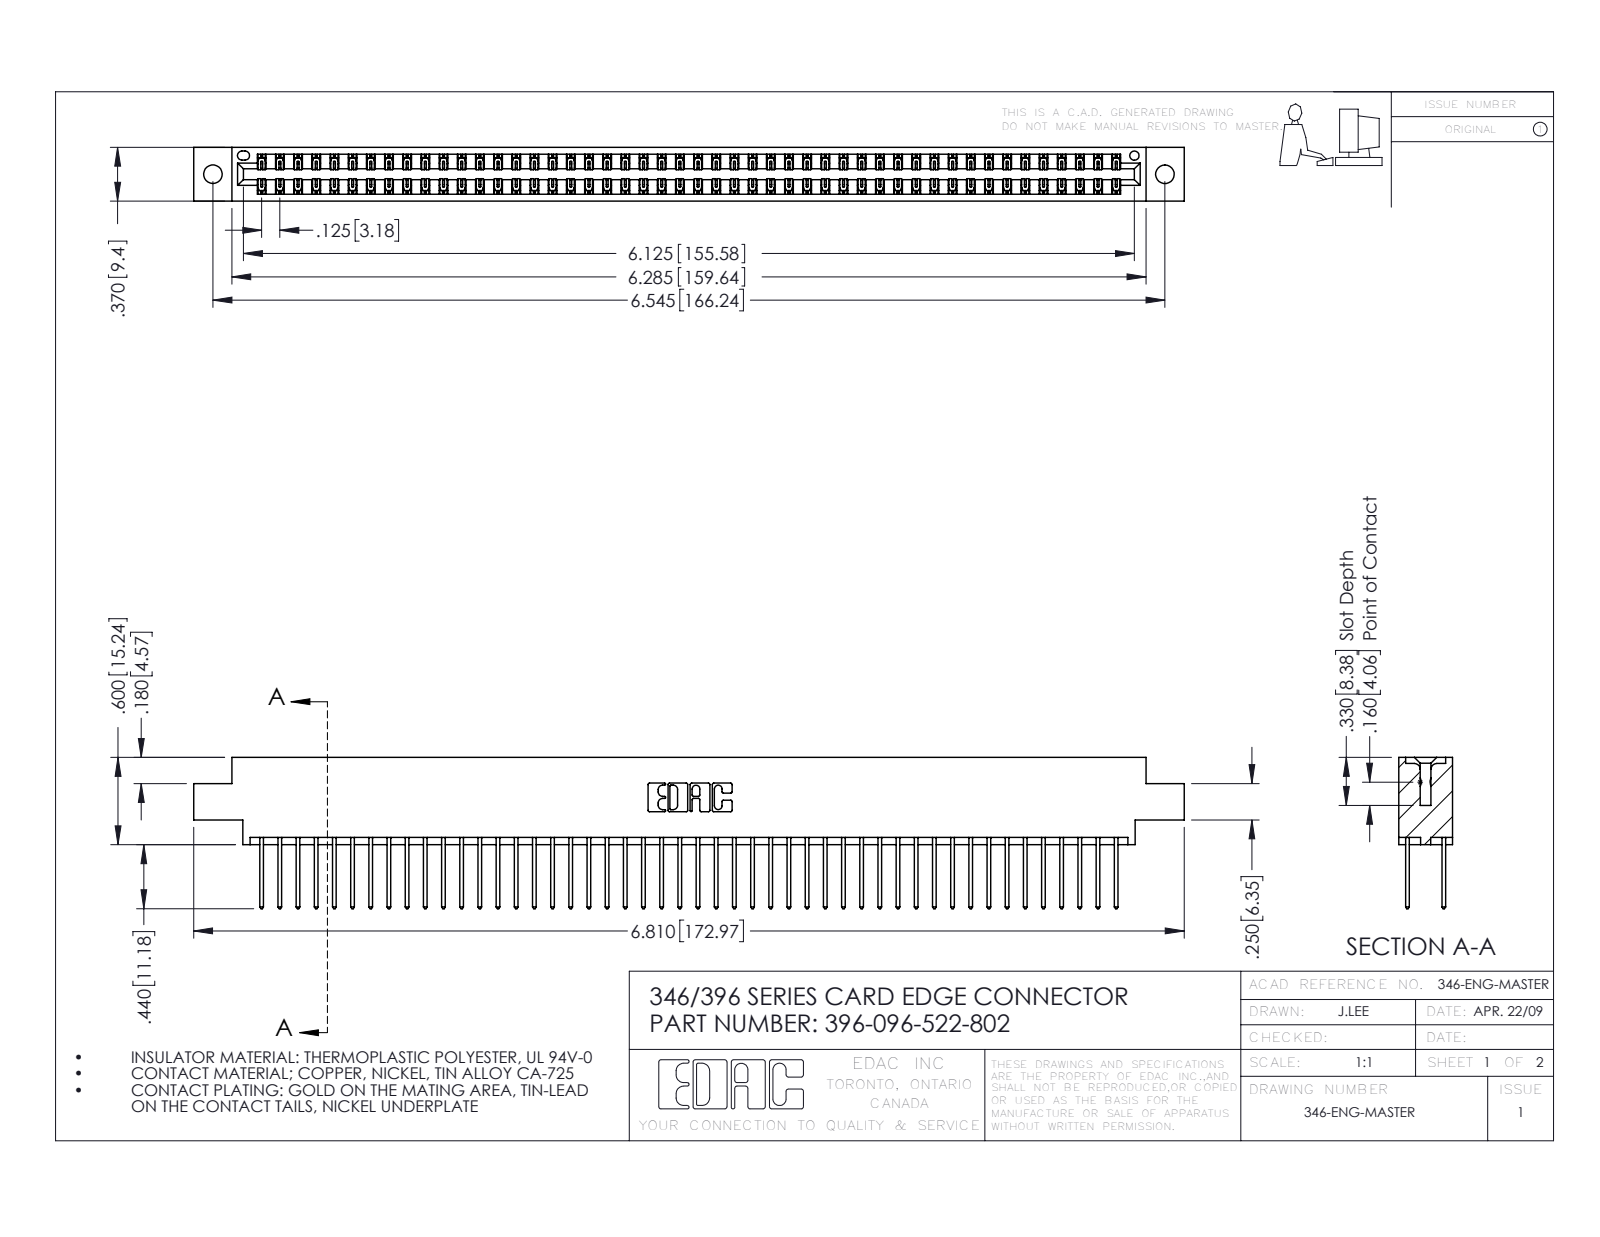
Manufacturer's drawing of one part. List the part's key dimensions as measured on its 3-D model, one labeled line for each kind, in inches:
Part name (STEP PRODUCT): 396-096-522-802; 346 Part_0.170 Offset - 0.128 Dia; 345-292-001_345-293-122
STEP written by: SolidWorks 2016 (CONFIG_CONTROL_DESIGN)
Units: inches
Bodies: 97 solids, 5118 faces (3440 planar, 1678 cylindrical, 0 other)
Overall size (bounding box): 6.81 × 1.04 × 0.37
Volume: 1.035 in³ · Surface area: 37.93 in²
Round holes (diameter × count): ⌀0.128 ×2, ⌀0.064 ×1
Partial cylindrical surfaces — rounded edges, fillets, slot ends (radius × count): R0.006 ×144, R0.01 ×96, R0.01 ×22, R0.007 ×6, R0.031 ×6, R0.026 ×3, R0.014 ×2, R0.022 ×2
Main face-to-face distances: 0.048, 0.322, 0.25, 0.37, 0.072, 0.298, 0.025, 0.275, 0.148, 0.222
Hole centre spacings: 0.246, 6.336, 6.545
